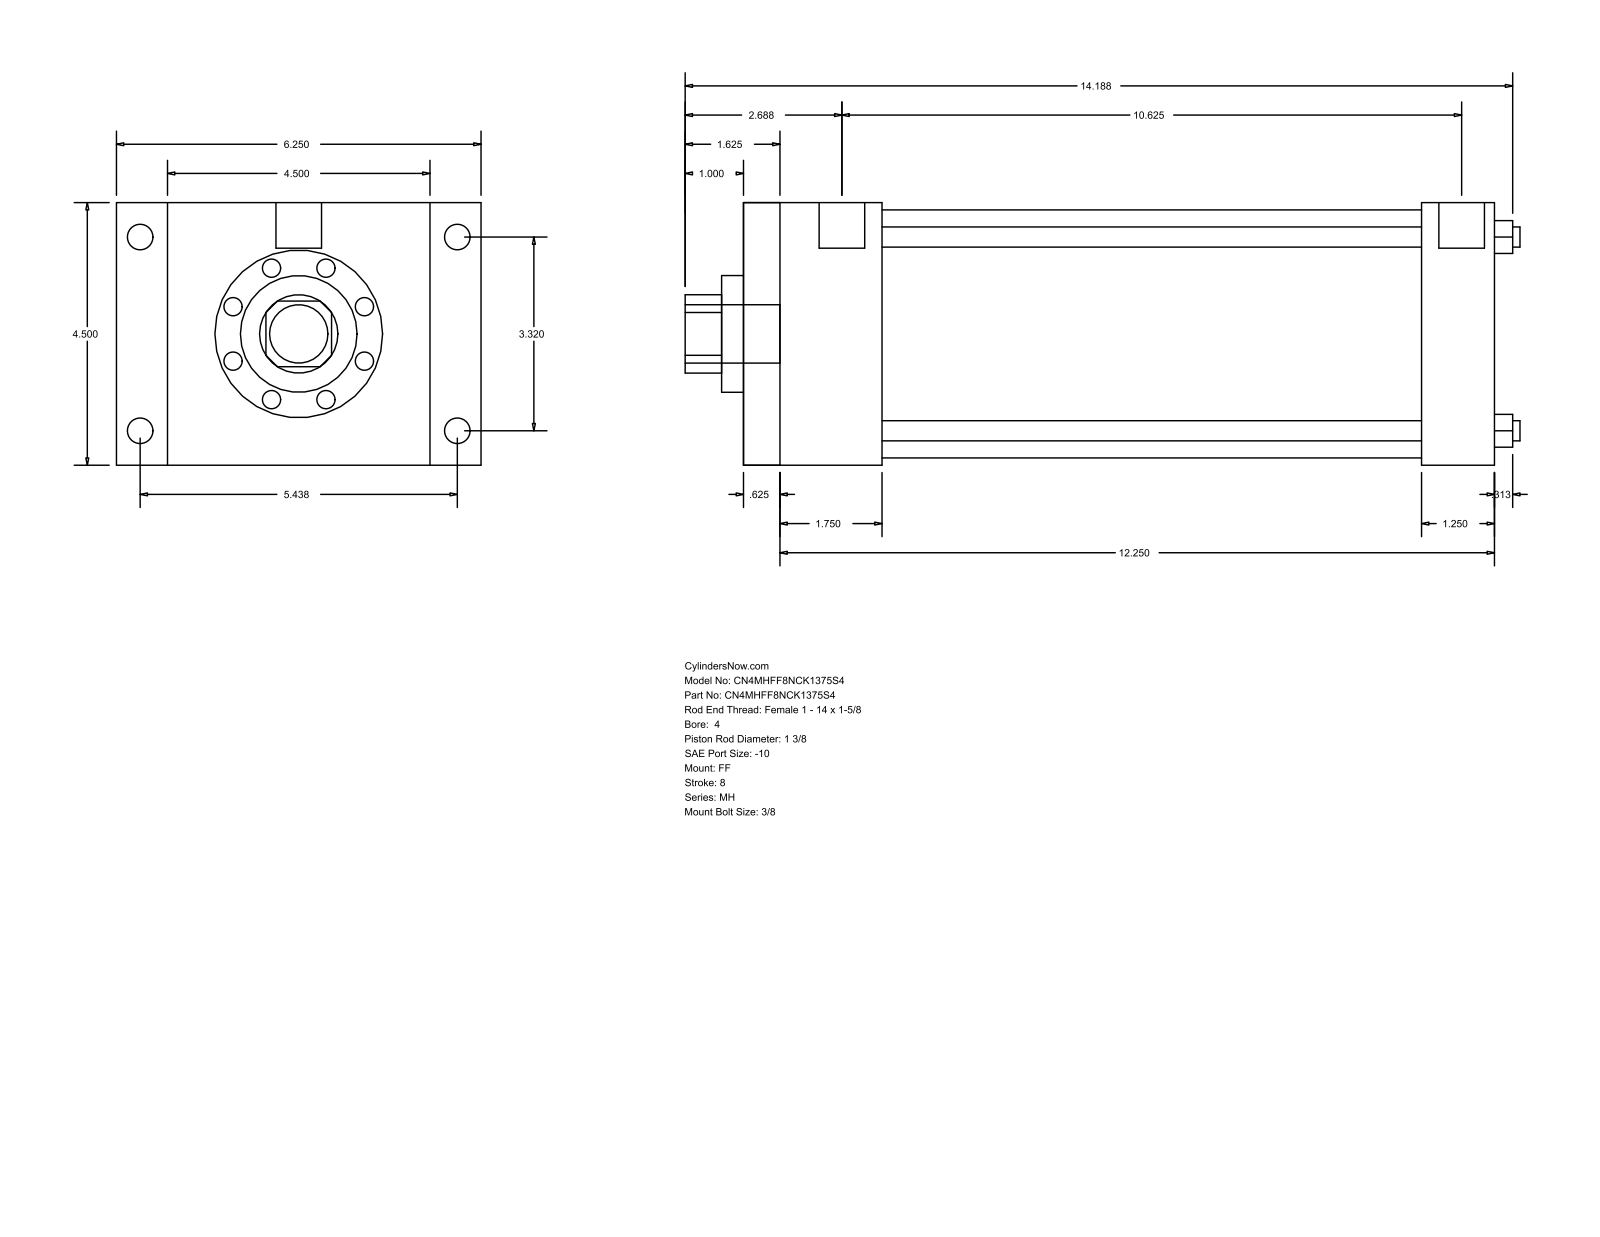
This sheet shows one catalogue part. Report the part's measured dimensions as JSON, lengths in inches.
{"part_name": "MH_FF__0400_1.375", "step_written_by": "GSSL Pune (CONFIG_CONTROL_DESIGN)", "units": "inches", "bodies": {"solids": 0, "faces": 92, "planar": 64, "cylindrical": 28, "other": 0}, "overall_size": [14.313, 6.25, 4.5], "round_holes": [[0.345, 4], [1.375, 1], [2, 1], [4.25, 1]], "round_bosses_or_shafts": [[0.438, 4], [0.344, 4], [0.781, 2], [1, 1]], "partial_cylinders_radius": [[0.672, 1]], "face_to_face_distances": [4.5, 12.875, 0.625, 12.25, 2.375, 1.75, 10.5, 11.625, 11, 9.25], "hole_center_spacings": [2.347, 3.32, 4.695]}
